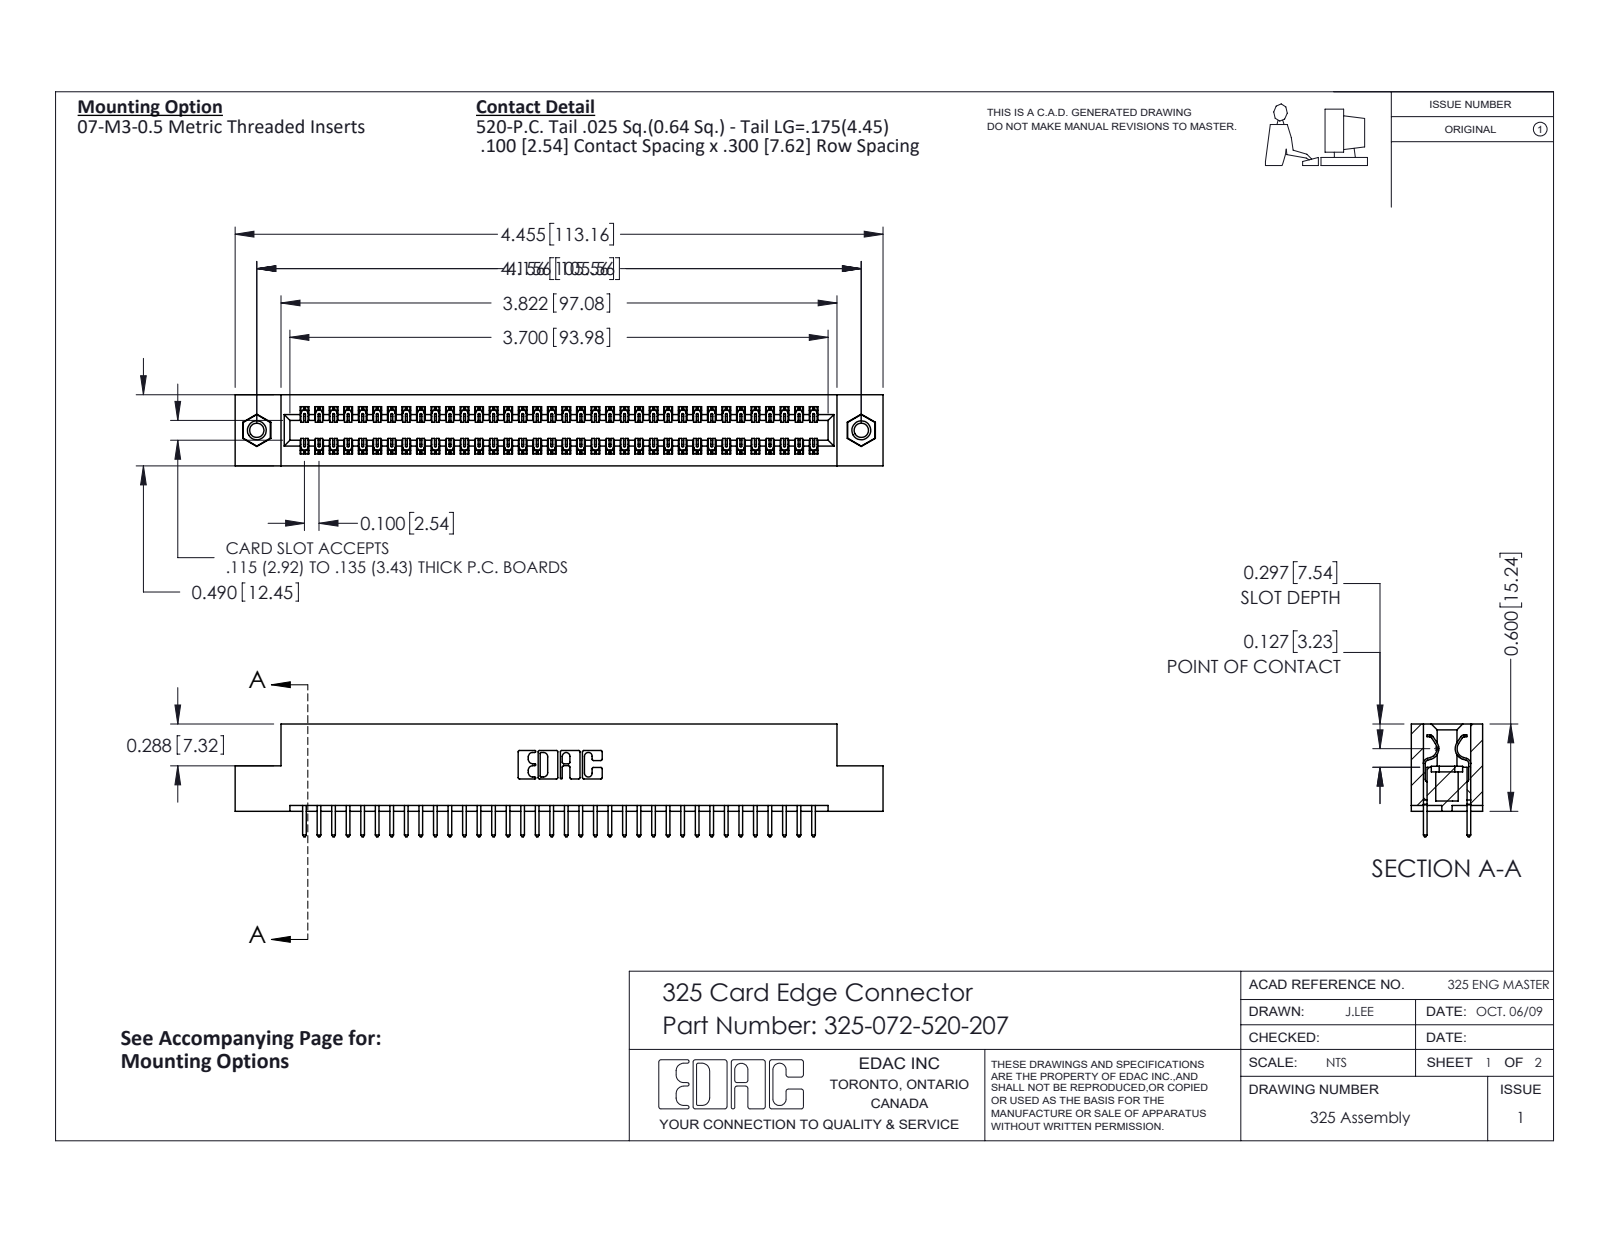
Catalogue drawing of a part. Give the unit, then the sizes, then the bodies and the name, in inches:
Units: inches
Overall size (bounding box): 4.455 × 0.775 × 0.49
Round holes (diameter × count): ⌀0.098 ×2, ⌀0.125 ×2, ⌀0.16 ×2
Round bosses / shafts (diameter × count): ⌀0.155 ×2
Partial cylindrical surfaces — rounded edges, fillets, slot ends (radius × count): R0.006 ×108, R0.01 ×72, R0.01 ×22, R0.007 ×6, R0.031 ×6, R0.026 ×3, R0.014 ×2, R0.022 ×2
Main face-to-face distances: 0.083, 0.407, 0.49, 0.3, 0.107, 0.383, 0.025, 0.325, 0.275, 0.56
Hole centre spacings: 4.156
Volume: 0.887 in³ · Surface area: 26.85 in²
Bodies: 75 solids, 3918 faces (2694 planar, 1208 cylindrical, 16 other)
Part name (STEP PRODUCT): 325-292-001_325-293-120; 345-250-001_345-250-005-103; 325 Part_TI; 325-072-520-207
STEP written by: SolidWorks 2016 (CONFIG_CONTROL_DESIGN)
